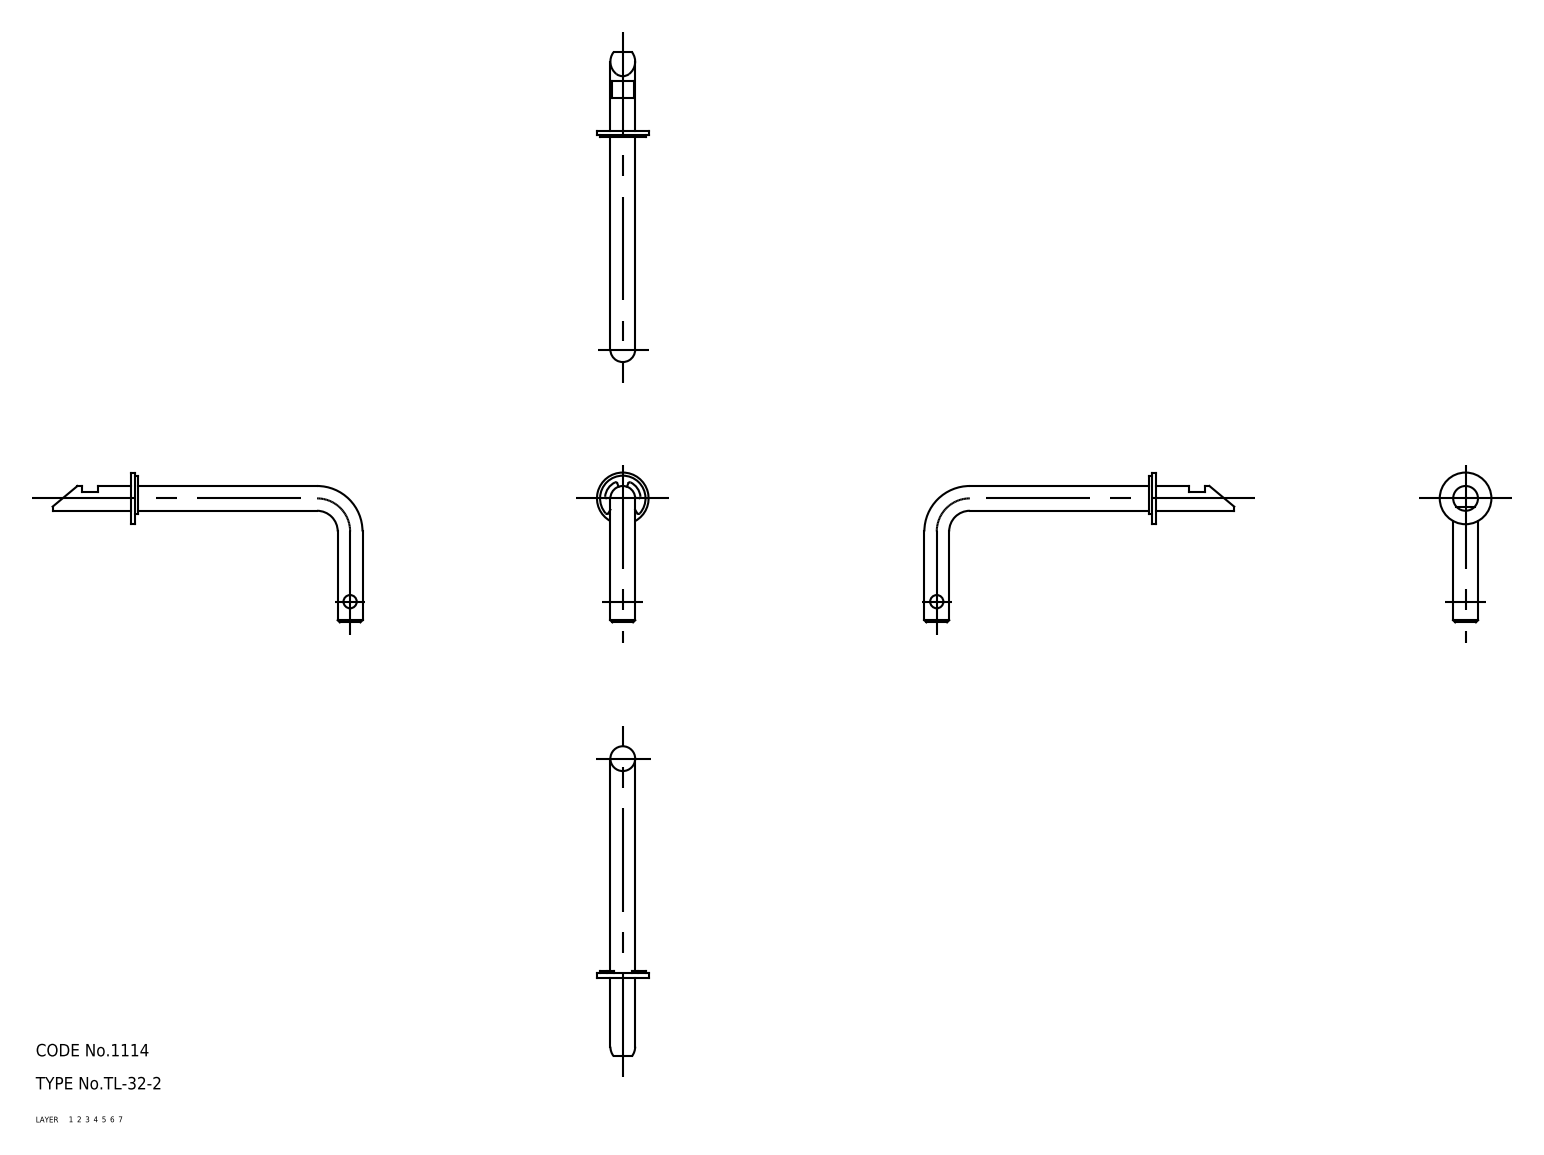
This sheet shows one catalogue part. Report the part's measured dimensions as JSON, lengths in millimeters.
{"part_name": "retainer; packing; handle; TL_32_2_10734_36", "step_written_by": "CADfix (AUTOMOTIVE_DESIGN)", "units": "millimeters", "bodies": {"solids": 3, "faces": 48, "planar": 0, "cylindrical": 0, "other": 48}, "overall_size": [75, 36.25, 12.5], "volume_mm3": 2772, "surface_area_mm2": 2289}
